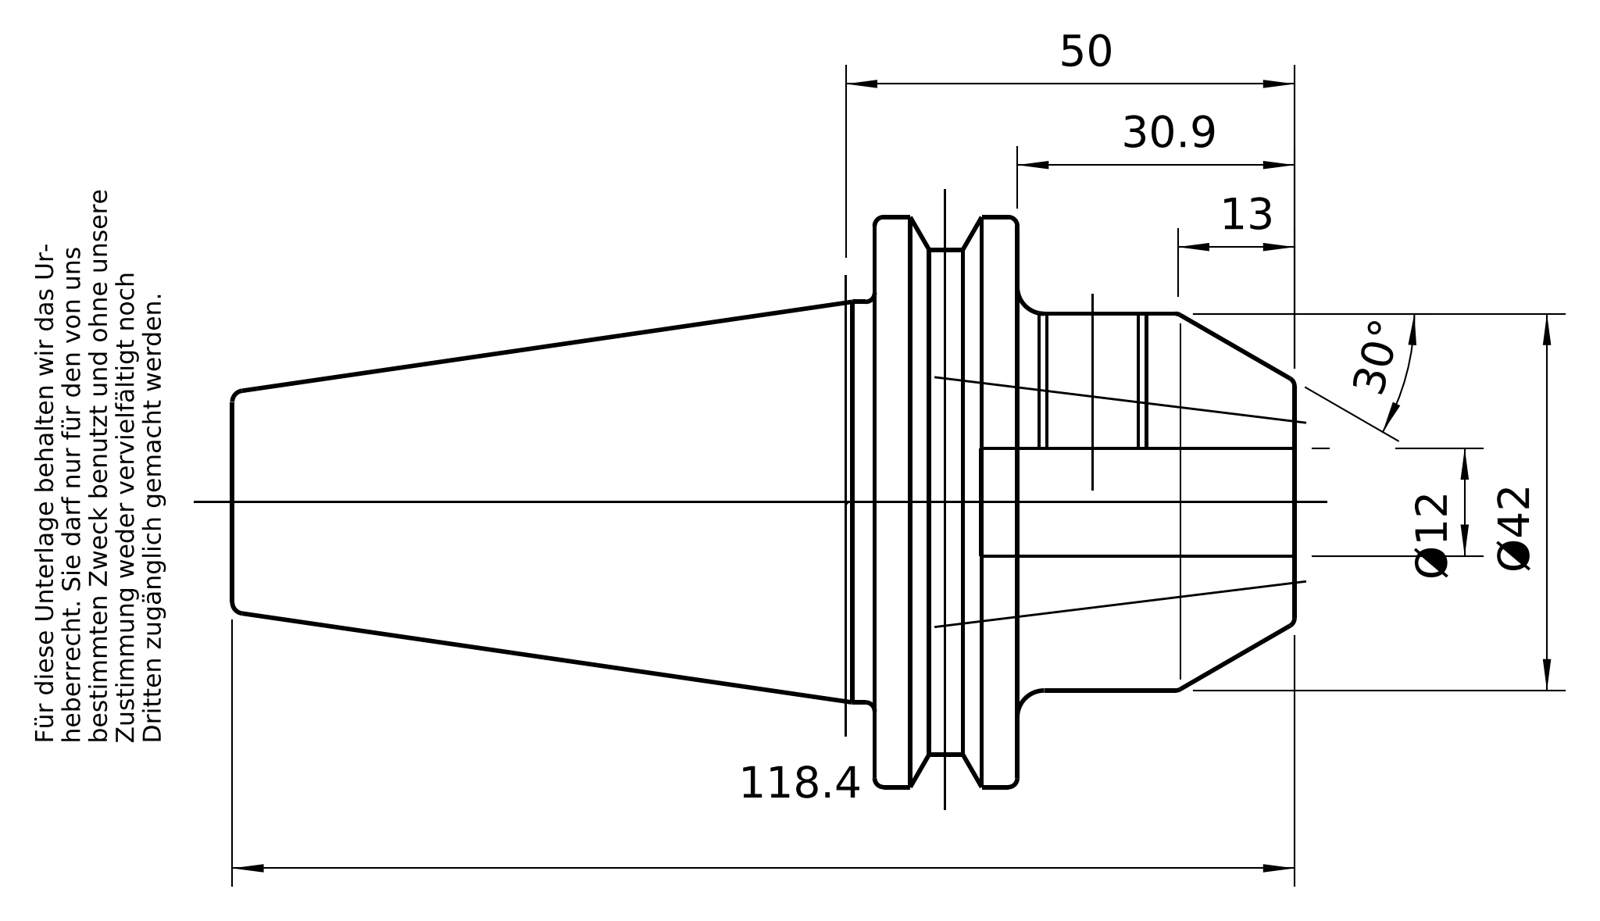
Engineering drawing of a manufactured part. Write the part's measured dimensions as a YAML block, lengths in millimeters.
part_name: "40-300-12"
step_written_by: "PRO/ENGINEER BY PARAMETRIC TECHNOLOGY CORPORATION, 2010430 (CONFIG_CONTROL_DESIGN)"
units: millimeters
bodies: {solids: 1, faces: 99, planar: 21, cylindrical: 28, other: 50}
overall_size: [118.25, 63.52, 61.42]
volume: 137737
surface_area: 25370
round_holes:
  - {diameter: 12, count: 2}
  - {diameter: 10.2, count: 1}
  - {diameter: 13.84, count: 1}
  - {diameter: 17.01, count: 1}
  - {diameter: 17.5, count: 1}
round_bosses_or_shafts:
  - {diameter: 43.75, count: 1}
  - {diameter: 42, count: 1}
  - {diameter: 16.01, count: 1}
partial_cylinders:
  - {radius: 1.35, count: 1}
  - {radius: 28, count: 1}
  - {radius: 31.76, count: 1}
face_to_face_distances: [15.85, 46.8, 30.95, 47.4, 16.2, 71.45, 87.3, 118.25, 83.25, 11.8]
